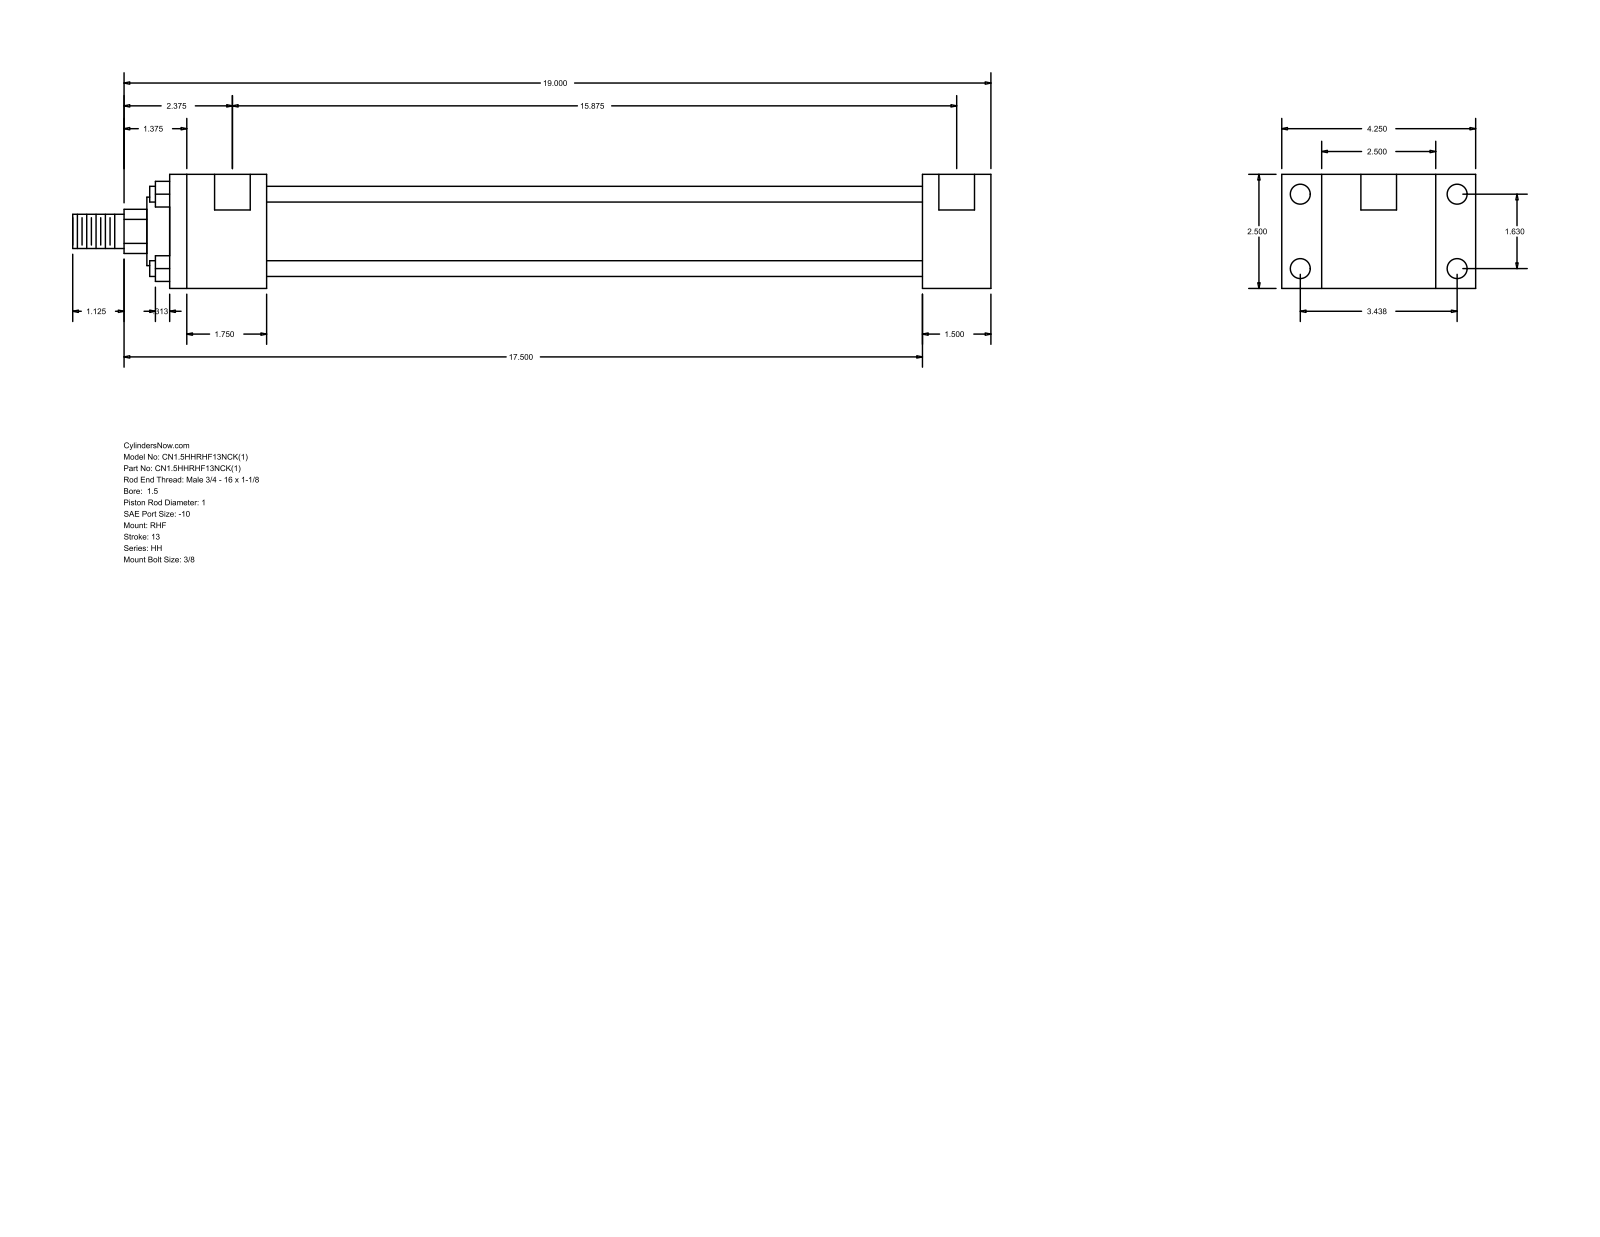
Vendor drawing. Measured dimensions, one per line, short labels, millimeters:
name: HH_RHF__0150_1
written by: GSSL Pune (CONFIG_CONTROL_DESIGN)
unit: mm
bodies: 0 solids, 88 faces (60 planar, 28 cylindrical, 0 other)
size: 511.18 × 107.95 × 63.5
holes: 4× ⌀5.56, 4× ⌀11.13, 2× ⌀19.84
bosses: 4× ⌀8.76, 1× ⌀44.45, 1× ⌀38.1, 1× ⌀25.4, 1× ⌀19.05
rounds: 1× R12.29
face distances: 63.5, 22.23, 85.73, 38.1, 107.96, 365.12, 403.22, 53.98, 419.1, 457.2
hole spacings: 1.59, 41.4, 87.32, 96.64, 404.81, 406.4, 403.22
